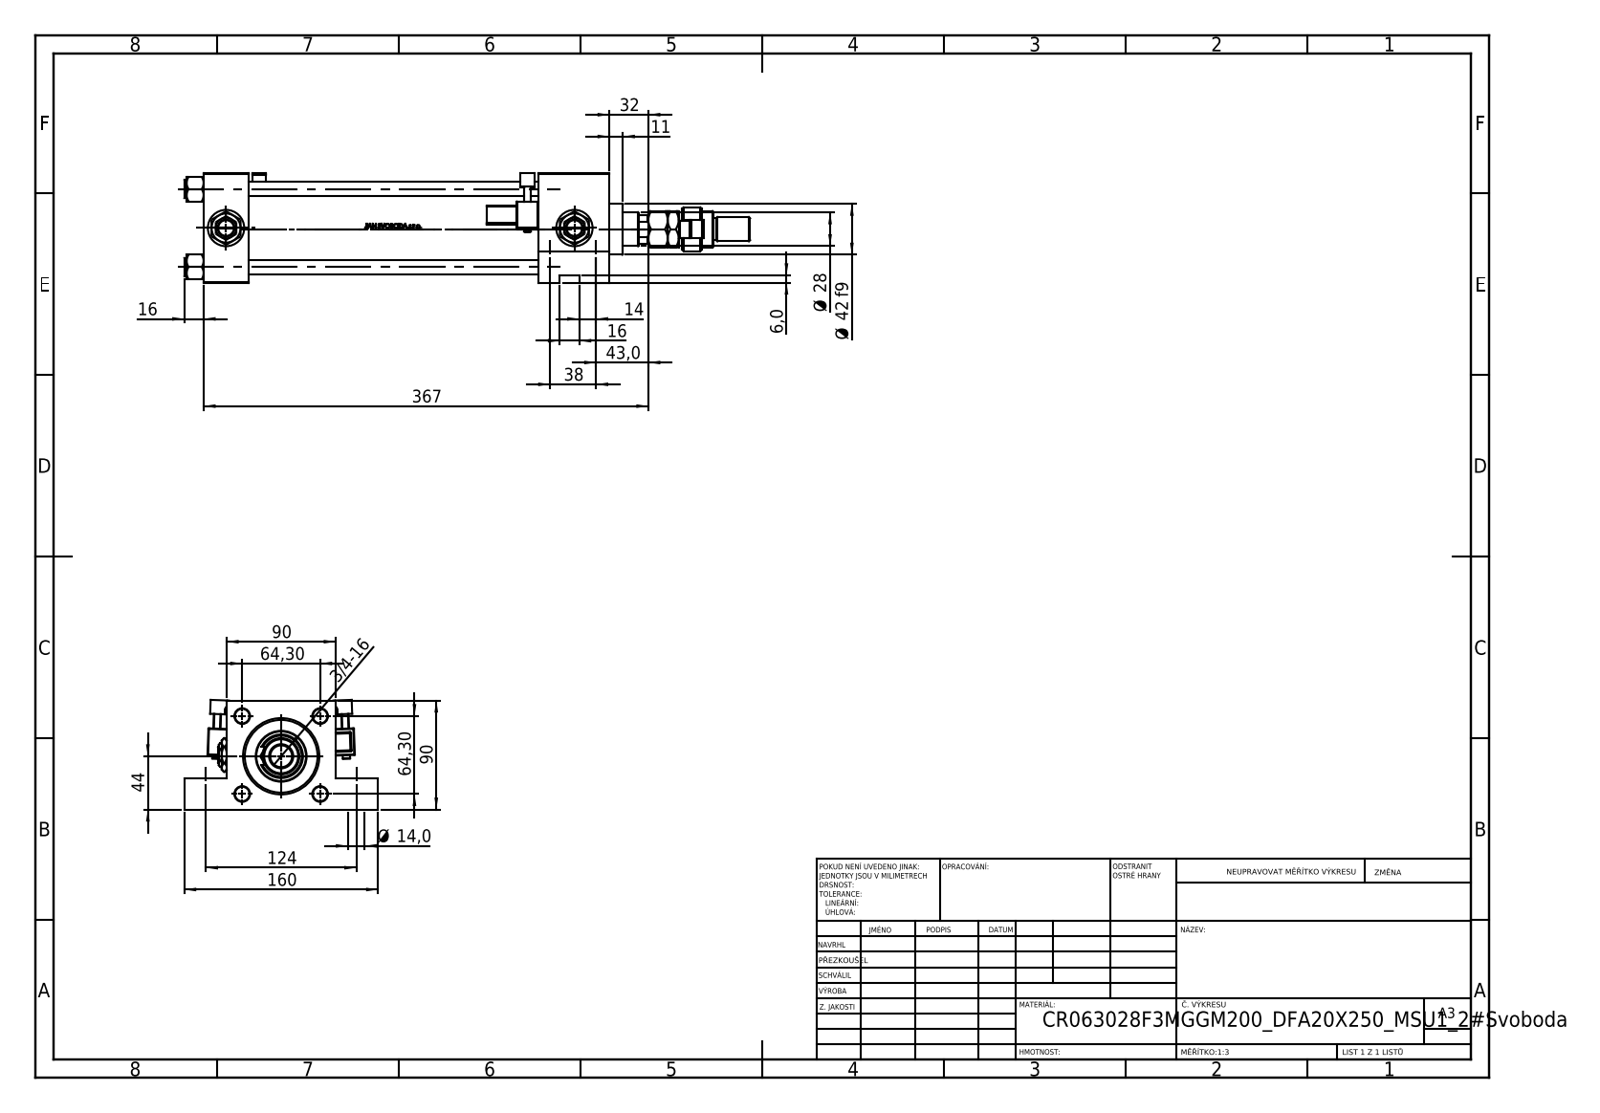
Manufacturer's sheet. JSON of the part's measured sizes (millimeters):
{"part_name": "V215CR_F_Body; V215CR_VCP_F; MFA; Zatka_pro_OIL_PORT (+5 more)", "step_written_by": "SolidWorks 2019 (CONFIG_CONTROL_DESIGN)", "units": "millimeters", "bodies": {"solids": 17, "faces": 1442, "planar": 571, "cylindrical": 209, "other": 662}, "overall_size": [467, 160, 90.53], "volume_mm3": 1417000, "surface_area_mm2": 341888, "round_holes": [[12, 4], [14, 4], [20.96, 4], [30, 4], [7, 3], [18.5, 1], [28, 1], [31, 1], [50, 1], [60, 1], [63, 1]], "round_bosses_or_shafts": [[15, 4], [6, 2], [69, 1], [42, 1], [36, 1], [30, 1], [22, 1], [20, 1]], "partial_cylinders_radius": [[0.5, 48], [1, 2], [2.5, 2], [4, 2], [7.5, 1], [12, 1], [13.5, 1]], "face_to_face_distances": [90, 37, 335, 298, 59, 276, 239, 26, 64, 35], "hole_center_spacings": [64.3, 38, 44.77, 46.18, 62.8, 68.03, 90.93, 124]}
